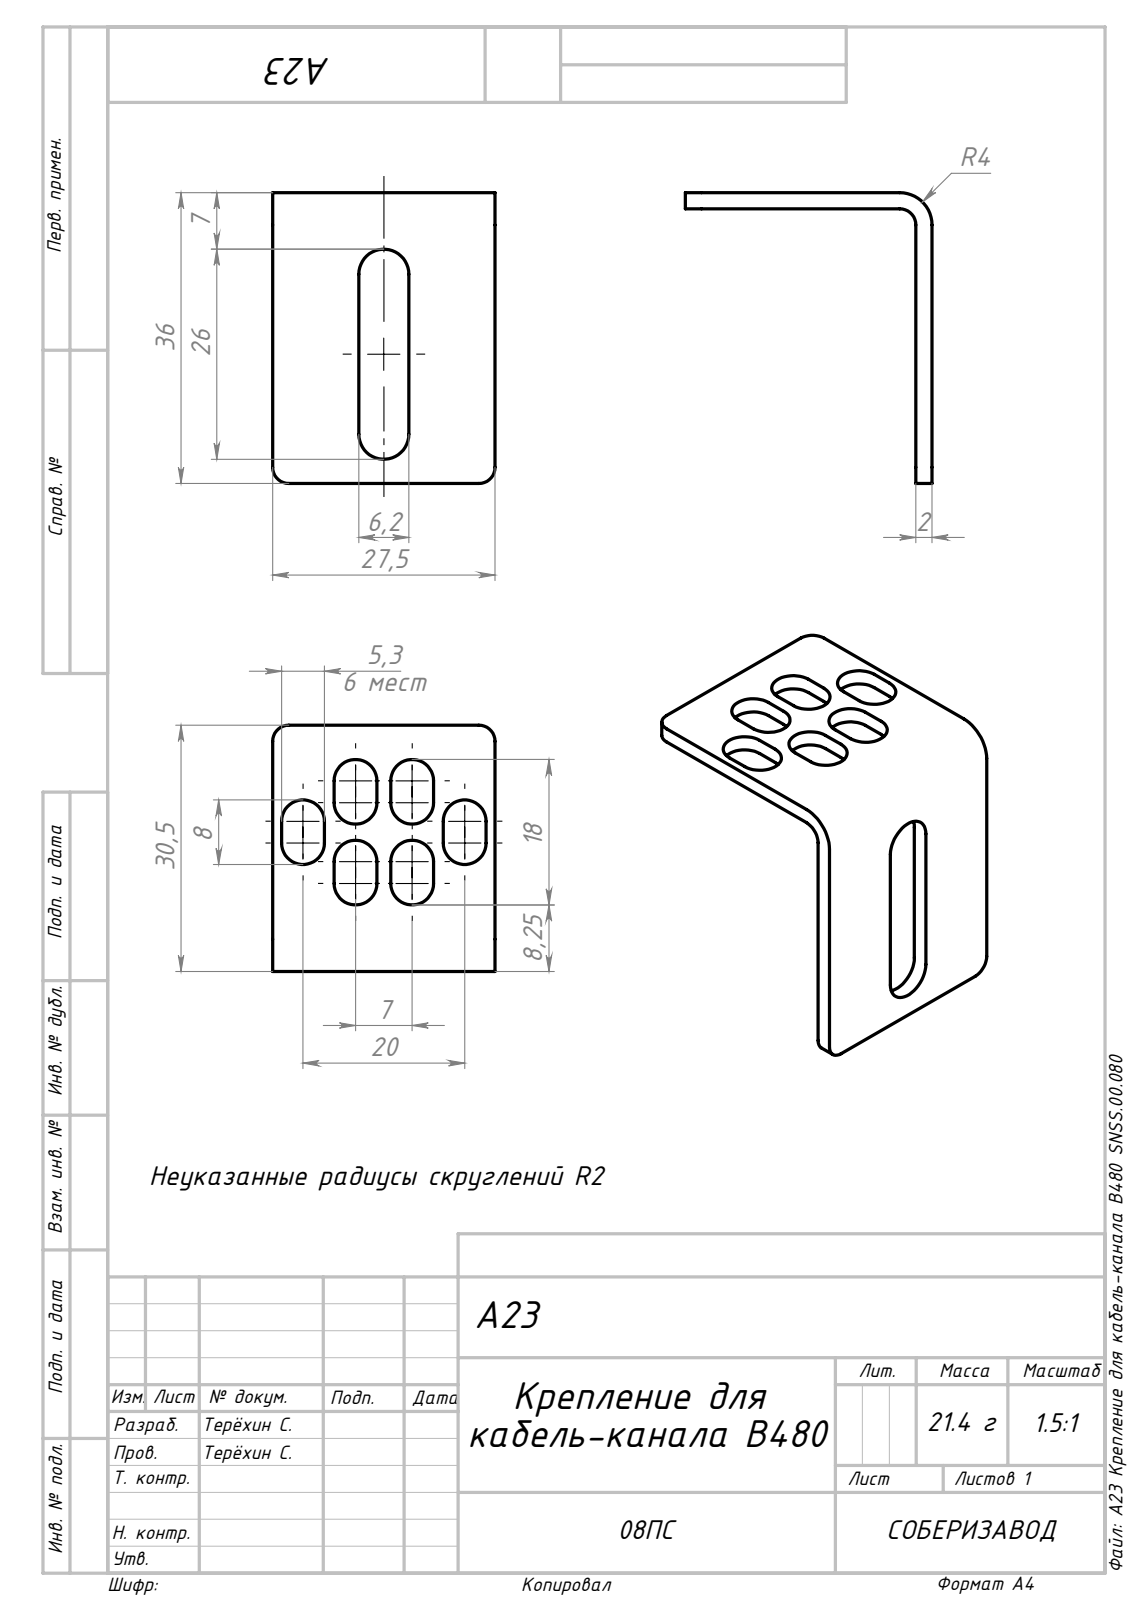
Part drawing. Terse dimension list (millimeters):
name: A23 Крепление для кабель-канала B480 SNSS.00.080_1; Сборка1
written by: SolidWorks 2024 (AUTOMOTIVE_DESIGN)
unit: mm
bodies: 1 solid, 53 faces (26 planar, 27 cylindrical, 0 other)
size: 36 × 30.5 × 27.5
volume: 2 727 mm³; area: 3 466 mm²
rounds: 12× R2.65, 5× R2, 2× R3.1, 1× R4
face distances: 2, 27.5, 10.65, 16.85, 34, 36, 28.5, 30.5, 6.2, 5.3
